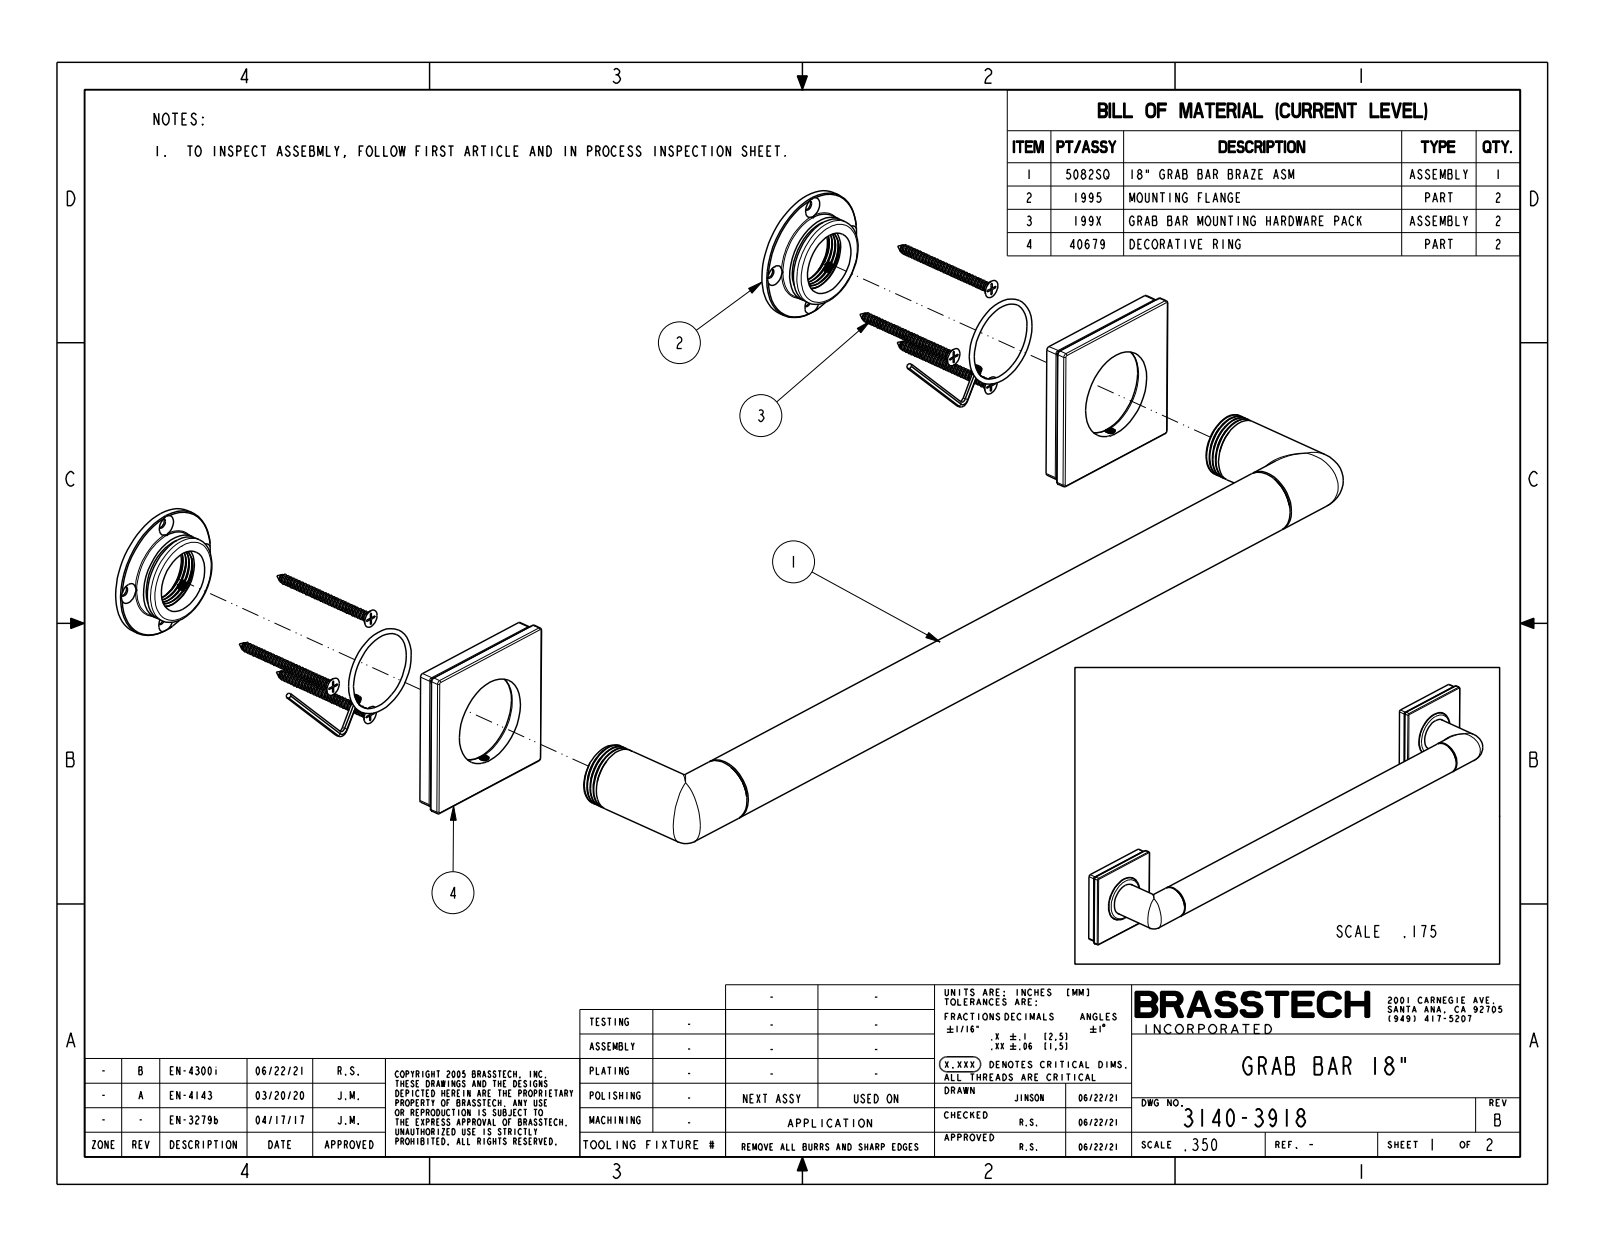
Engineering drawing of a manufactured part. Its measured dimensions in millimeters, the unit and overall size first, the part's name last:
Units: millimetres
Overall size (bounding box): 533.4 × 76.2 × 70
Round bosses / shafts (diameter × count): ⌀31.8 ×3, ⌀44.5 ×2
Partial cylindrical surfaces — rounded edges, fillets, slot ends (radius × count): R1.5 ×16, R0.8 ×12, R2.3 ×6
Main face-to-face distances: 13.3, 1.3, 74.9, 73.7, 457.2, 76.2, 15.2, 1.9, 458.5, 532.1
Volume: 577 300 mm³ · Surface area: 82 390 mm²
Bodies: 1 solid, 168 faces (22 planar, 54 cylindrical, 92 other)
Part name (STEP PRODUCT): 3140-3918
STEP written by: CREO PARAMETRIC BY PTC INC, 2018400 (CONFIG_CONTROL_DESIGN)
